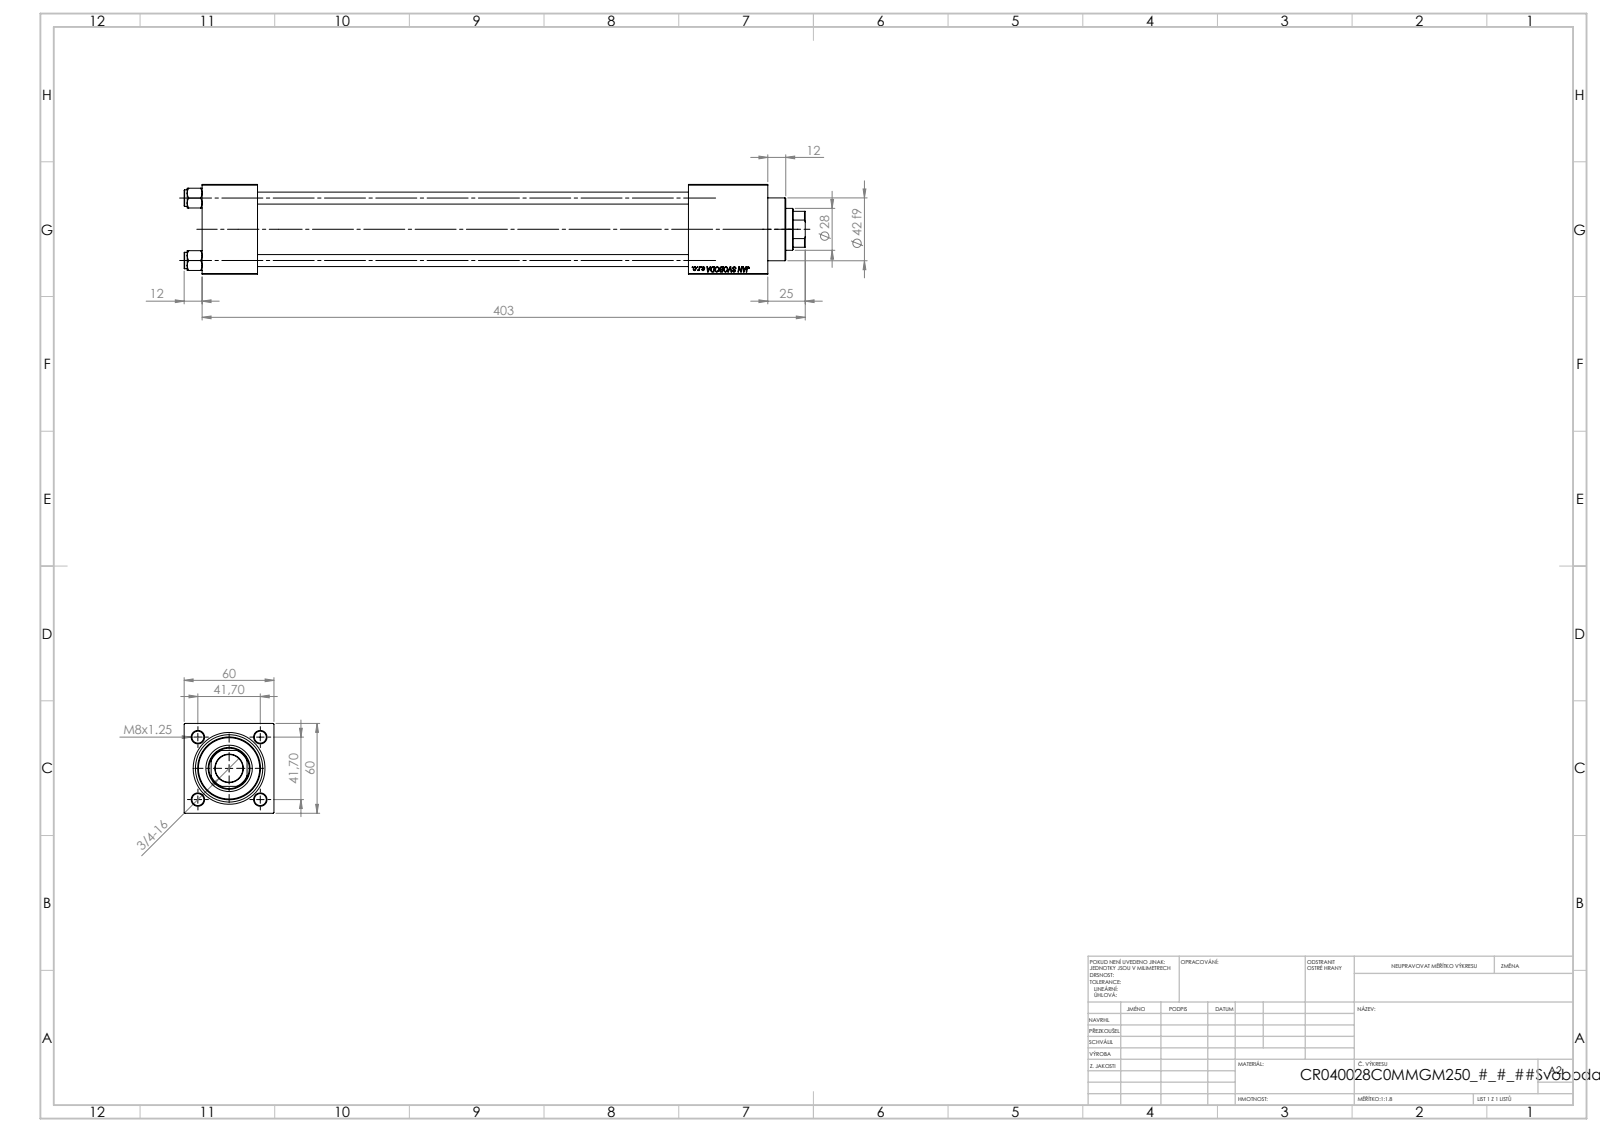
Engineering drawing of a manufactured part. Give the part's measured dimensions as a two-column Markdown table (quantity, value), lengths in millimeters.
| quantity | value |
| --- | --- |
| part name | NUT_M5_C; V215_VC_A; V215CR_C_TYCINKA; V215CR_C_Body (+1 more) |
| STEP written by | SolidWorks 2019 (CONFIG_CONTROL_DESIGN) |
| units | millimeters |
| bodies | 11 solids, 1148 faces (526 planar, 86 cylindrical, 536 other) |
| overall size | 415 × 60 × 60 |
| volume | 705 567 mm³ |
| surface area | 216 841 mm² |
| round holes (diameter × count) | 8 × 4, 7 × 2, 16.66 × 2, 24 × 2, 18.5 × 1, 28 × 1, 31 × 1, 40 × 1, 45 × 1 |
| round bosses / shafts (diameter × count) | 11 × 4, 46 × 1, 42 × 1 |
| partial cylindrical surfaces (radius × count) | 13.5 × 1 |
| main face-to-face distances | 60, 37, 325, 288, 349.3, 312.3, 24.3, 53, 378, 341 |
| hole center spacings | 29.49, 41.7, 58.97, 322.5 |
